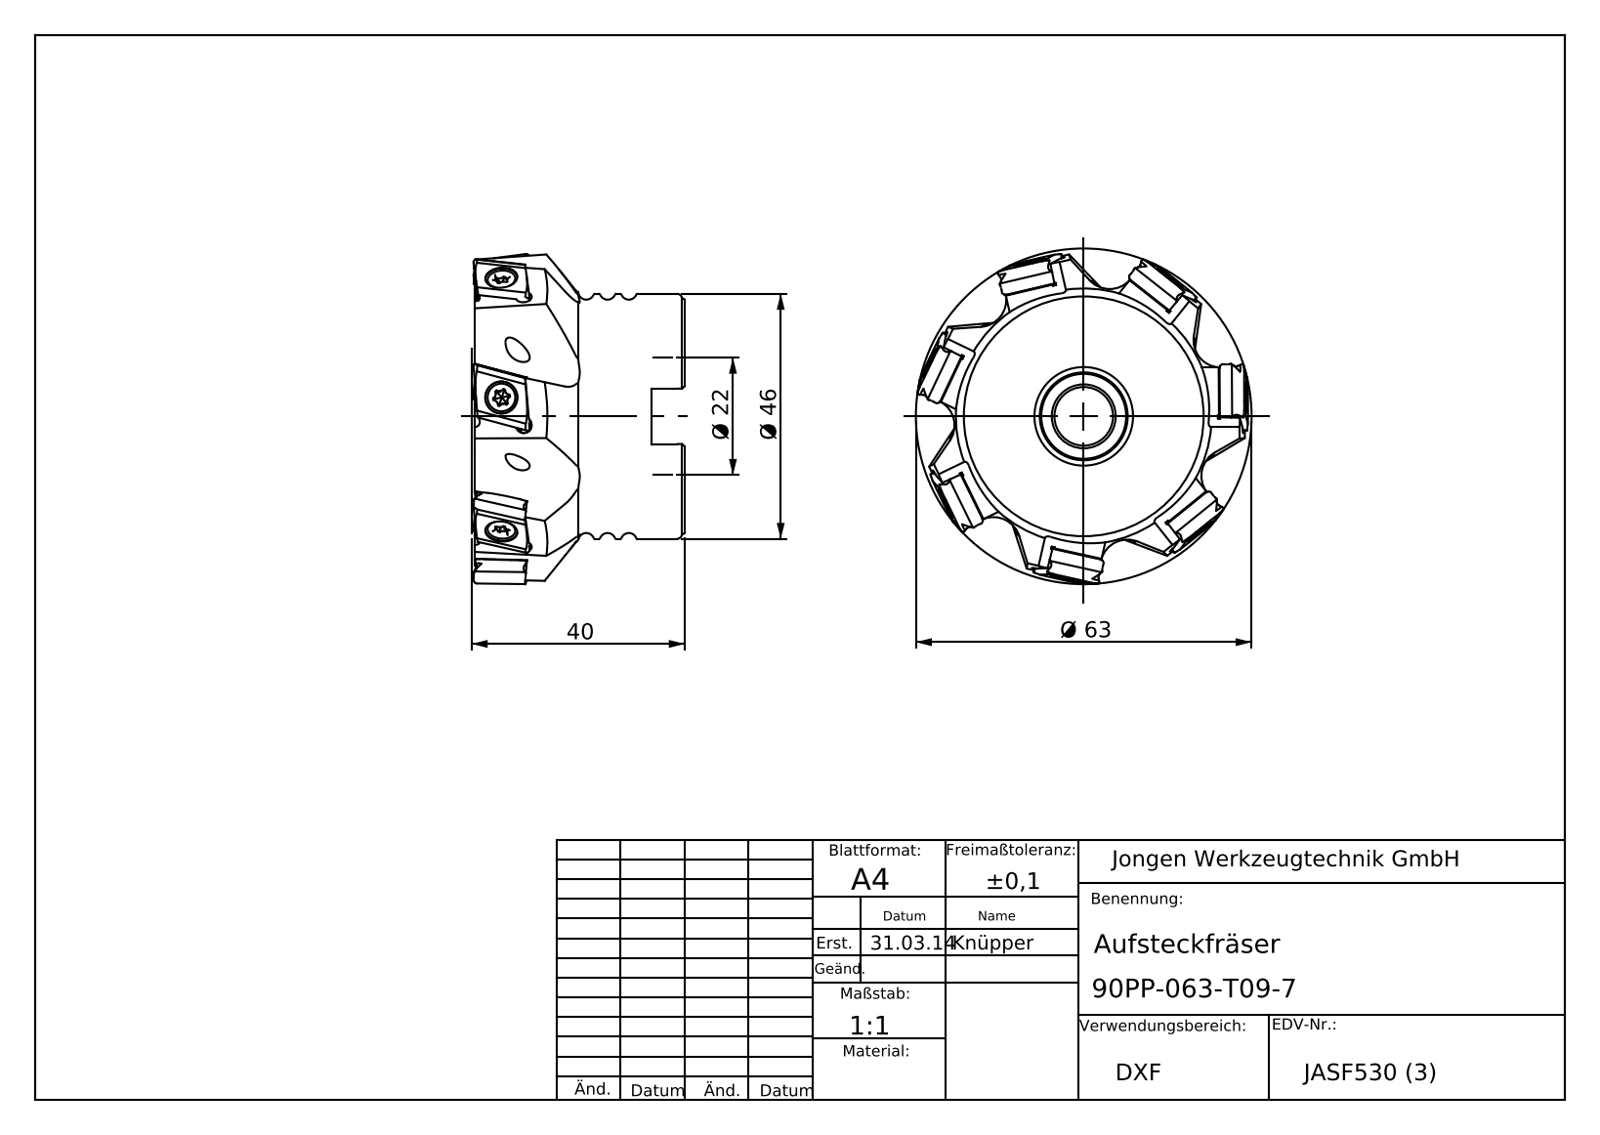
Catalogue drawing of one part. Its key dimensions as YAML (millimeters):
part_name: "90PP_063_T09_7"
step_written_by: "SolidWorks 2015 (AUTOMOTIVE_DESIGN)"
units: millimeters
bodies: {solids: 1, faces: 239, planar: 114, cylindrical: 80, other: 45}
overall_size: [63, 63, 40.1]
volume: 66828
surface_area: 17859
round_holes:
  - {diameter: 2.1, count: 9}
  - {diameter: 3.3, count: 9}
  - {diameter: 11, count: 1}
  - {diameter: 16.5, count: 1}
  - {diameter: 22, count: 1}
  - {diameter: 22.15, count: 1}
  - {diameter: 22.3, count: 1}
round_bosses_or_shafts:
  - {diameter: 46, count: 1}
partial_cylinders:
  - {radius: 0.9, count: 9}
  - {radius: 1.5, count: 9}
  - {radius: 2, count: 9}
  - {radius: 23.25, count: 1}
face_to_face_distances: [36.9, 20, 16.9, 6.3, 13.7, 30.6, 10.4, 39.4, 33.1, 19.4]
